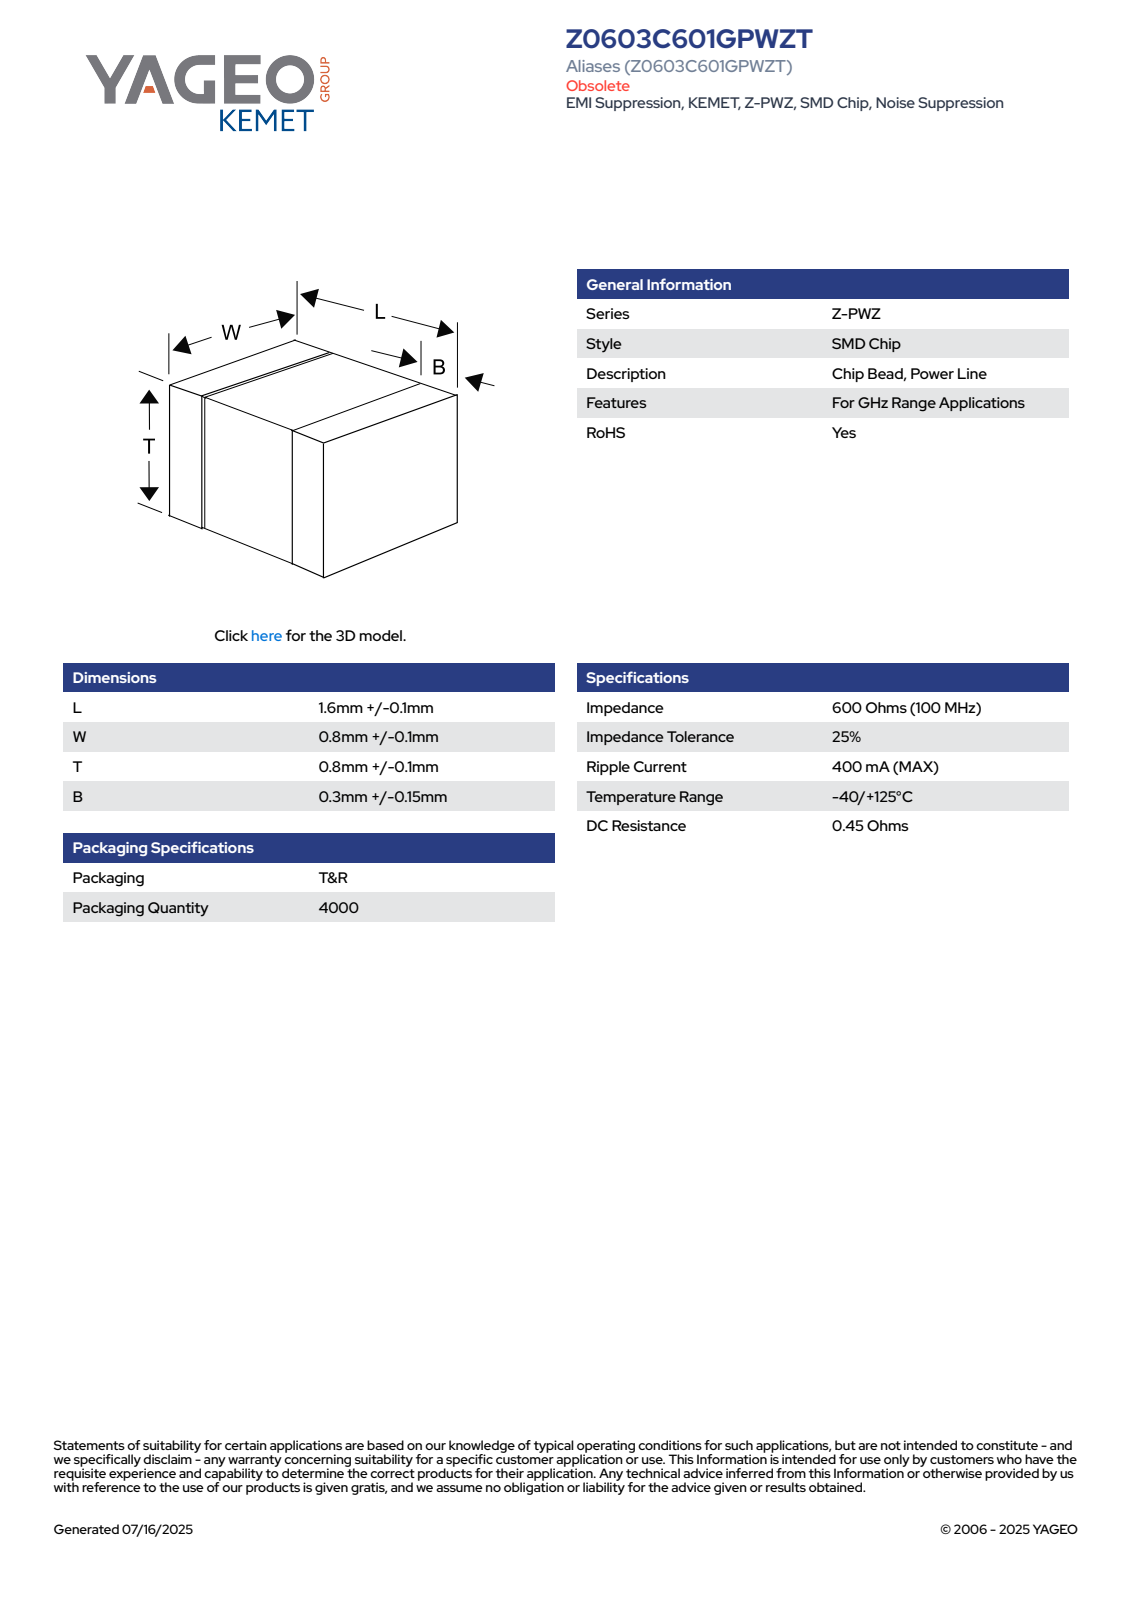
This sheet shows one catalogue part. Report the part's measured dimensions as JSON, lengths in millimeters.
{"part_name": "IS_KCS_0603_L1.7W0.9T0.9B0.45", "step_written_by": "SolidWorks 2014 (AUTOMOTIVE_DESIGN)", "units": "millimeters", "bodies": {"solids": 4, "faces": 73, "planar": 73, "cylindrical": 0, "other": 0}, "overall_size": [1.7, 0.9, 0.9], "volume_mm3": 1, "surface_area_mm2": 8, "face_to_face_distances": [0.88, 0.9, 0.86, 1.7, 0.45, 1.25, 0.8, 0.89, 0.87, 0.33]}
